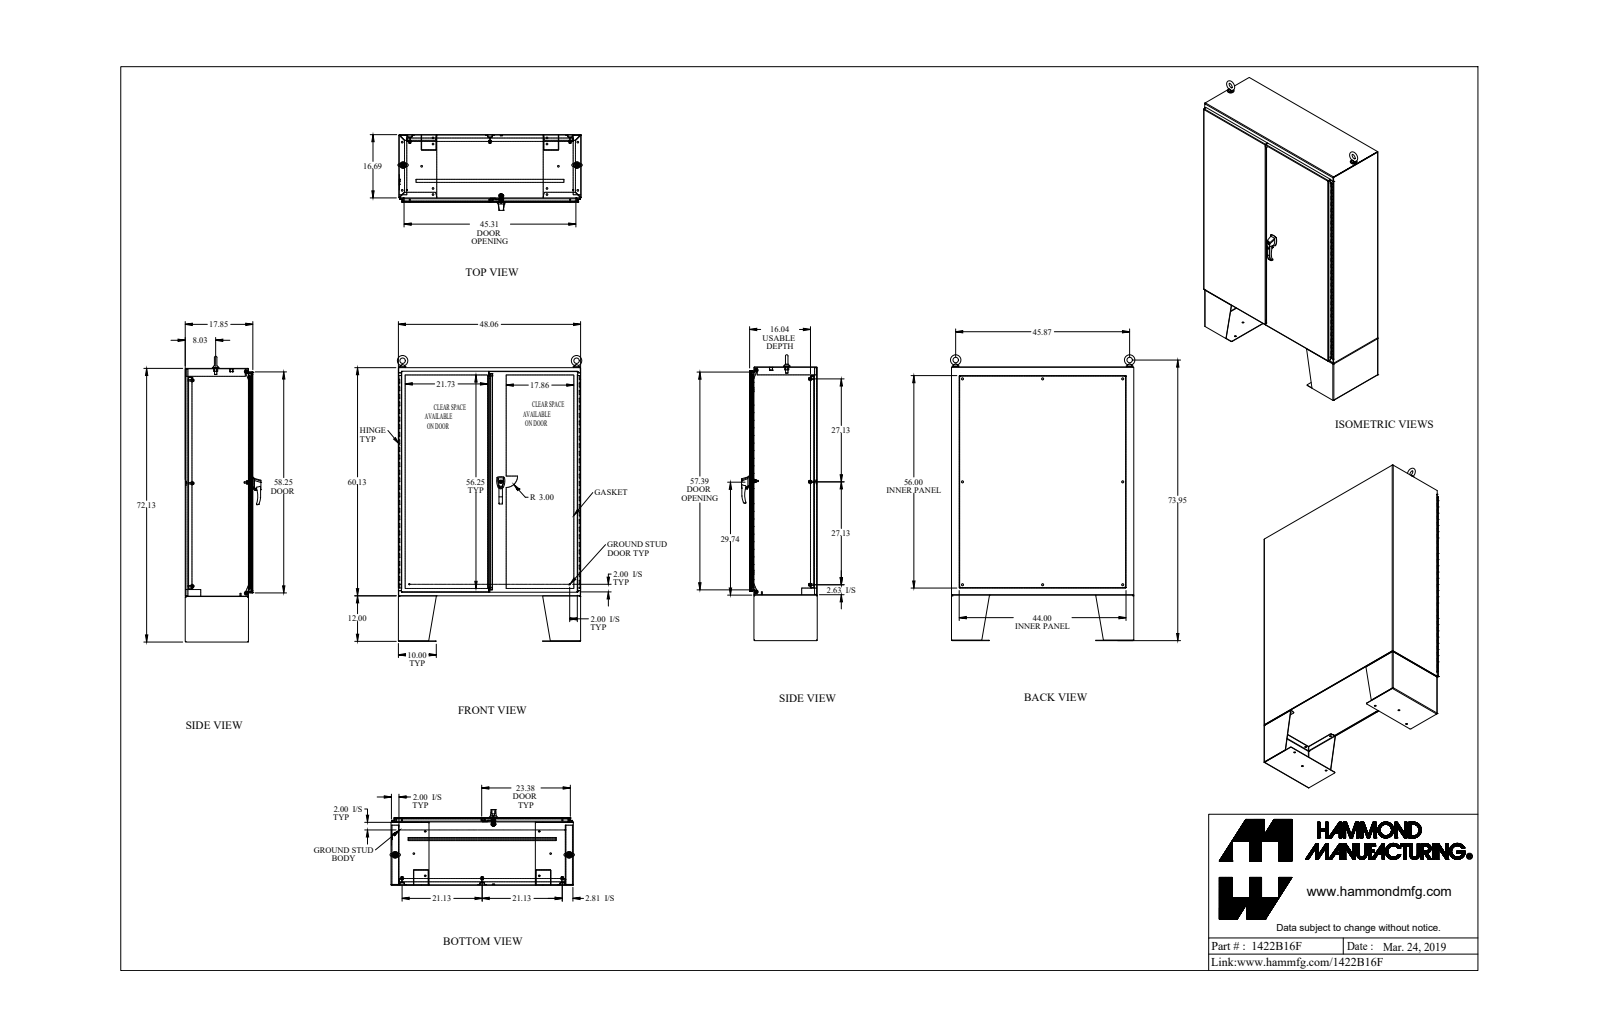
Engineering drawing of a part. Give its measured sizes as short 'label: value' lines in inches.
name: 1422B16F_Default
written by: SolidWorks 2019 (CONFIG_CONTROL_DESIGN)
unit: in
bodies: 90 solids, 2769 faces (1280 planar, 1242 cylindrical, 247 other)
size: 75.778 × 49.121 × 19.963
volume: 1 546 in³; area: 30 883 in²
holes: 20× ⌀0.304, 14× ⌀0.437, 9× ⌀0.307, 8× ⌀0.563, 6× ⌀0.445, 2× ⌀0.11, 2× ⌀0.25, 2× ⌀0.257, 2× ⌀0.28, 2× ⌀0.281, 2× ⌀0.313, 2× ⌀0.39
bosses: 10× ⌀1, 8× ⌀0.65, 8× ⌀0.375, 8× ⌀0.33, 6× ⌀0.281, 4× ⌀0.25, 2× ⌀1.75, 2× ⌀1.5
rounds: 32× R0.048, 32× R0.143, 22× R0.125, 16× R0.018, 14× R0.06, 12× R0.116, 8× R0.05, 8× R0.185
face distances: 0.095, 0.095, 17.658, 17.753, 17.753, 17.848, 0.125, 16.066, 15.971, 1.687
hole spacings: 6, 46.778, 12, 47.919, 18, 49.762, 24, 52.232
